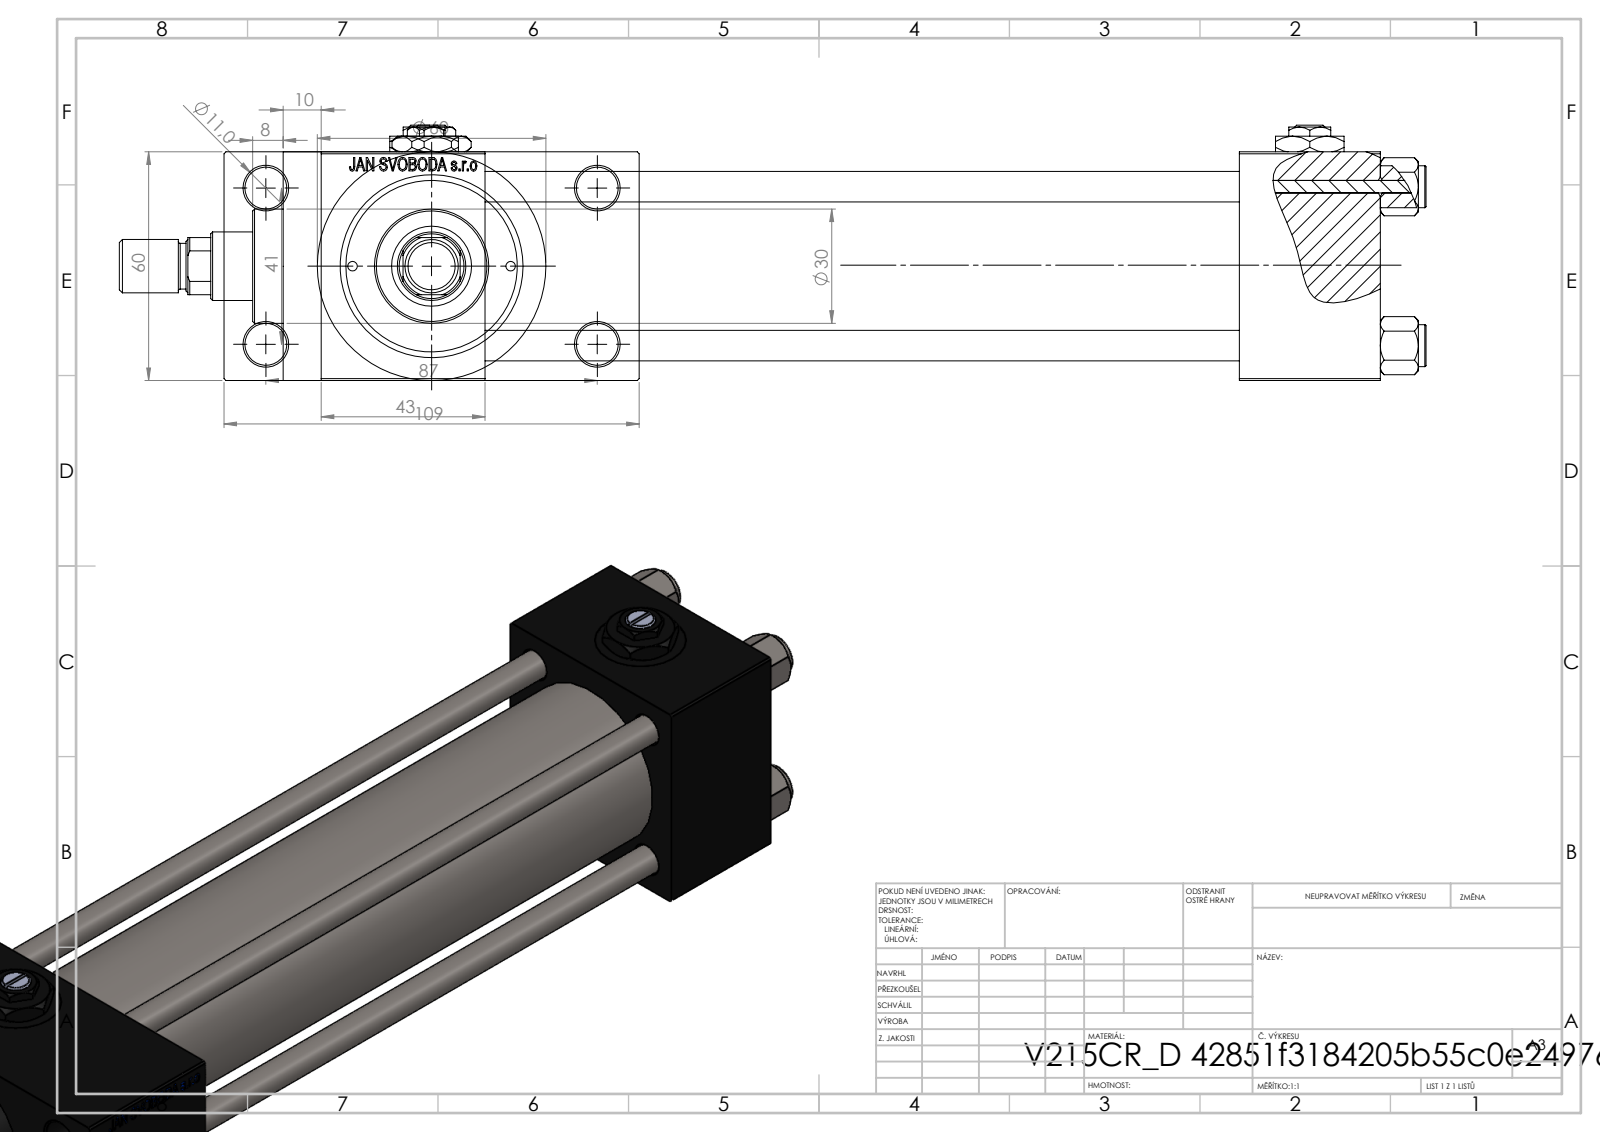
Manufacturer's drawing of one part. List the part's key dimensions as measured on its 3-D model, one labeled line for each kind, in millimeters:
Part name (STEP PRODUCT): Zatka_pro_OIL_PORT; V215CR_VCP_D; V215CR_D_TYCINKA; V215_VC_A (+3 more)
STEP written by: SolidWorks 2019 (CONFIG_CONTROL_DESIGN)
Units: millimetres
Bodies: 14 solids, 1227 faces (552 planar, 107 cylindrical, 568 other)
Overall size (bounding box): 343 × 109 × 67
Volume: 633 309 mm³ · Surface area: 186 091 mm²
Round holes (diameter × count): ⌀8 ×4, ⌀11 ×4, ⌀16.66 ×4, ⌀24 ×4, ⌀7 ×3, ⌀2.5 ×2, ⌀8.5 ×1, ⌀18 ×1, ⌀21 ×1, ⌀31 ×1, ⌀40 ×1, ⌀45 ×1
Round bosses / shafts (diameter × count): ⌀11 ×4, ⌀60 ×1, ⌀46 ×1, ⌀30 ×1, ⌀14 ×1, ⌀12 ×1
Partial cylindrical surfaces — rounded edges, fillets, slot ends (radius × count): R8.5 ×1
Main face-to-face distances: 60, 198, 24.5, 84.5, 37, 235, 43, 278, 241, 53
Hole centre spacings: 20.85, 22.65, 29.49, 30.62, 41.7, 46.53, 47.15, 48.09
